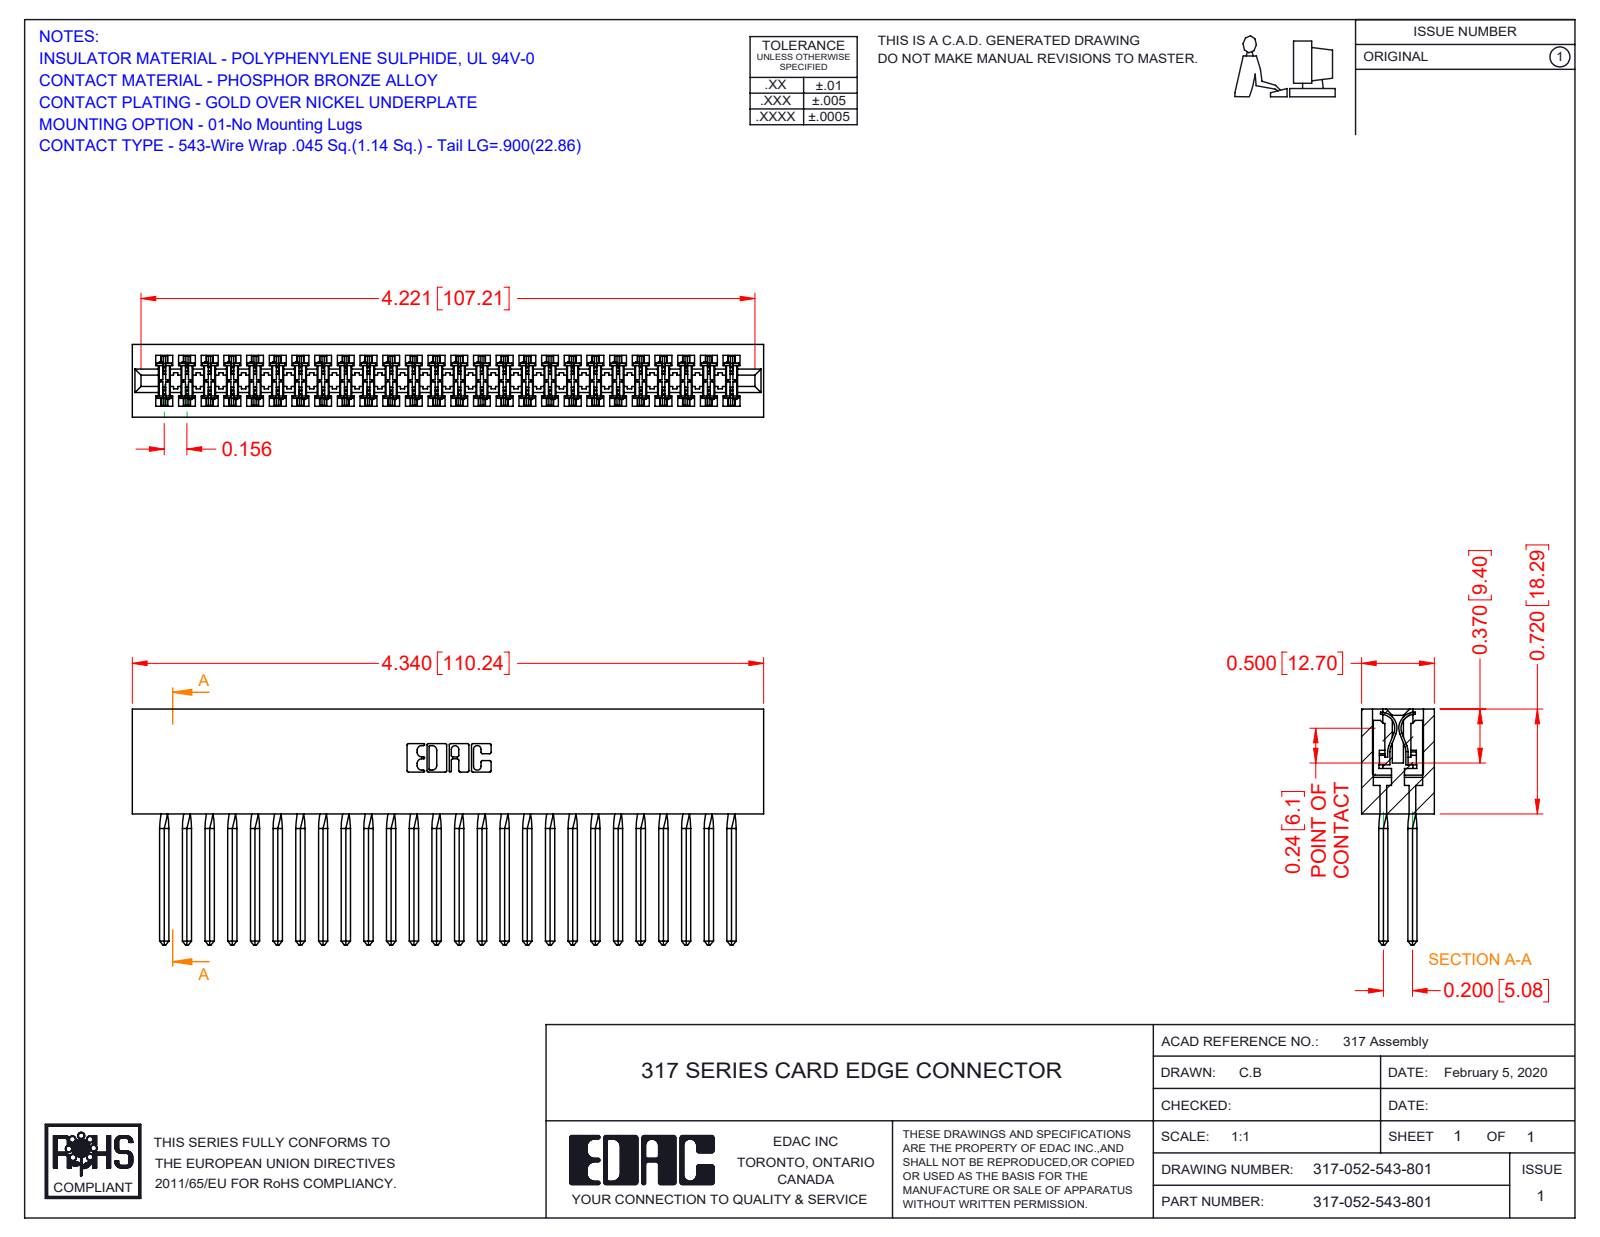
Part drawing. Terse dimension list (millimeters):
name: 317 Part_Lugless; 317-052-543-801; 317-290-001_543
written by: SolidWorks 2016 (CONFIG_CONTROL_DESIGN)
unit: mm
bodies: 53 solids, 4718 faces (3846 planar, 664 cylindrical, 208 other)
size: 110.2 × 41.1 × 12.7
volume: 20 010 mm³; area: 30 010 mm²
rounds: 104× R0.4, 22× R0.3, 6× R0.2, 6× R0.8, 3× R0.7, 2× R2.4, 2× R2.5, 2× R2.8
face distances: 1.9, 12.7, 10.8, 2.8, 8.9, 5, 2.4, 18.3, 5.1, 2.9
